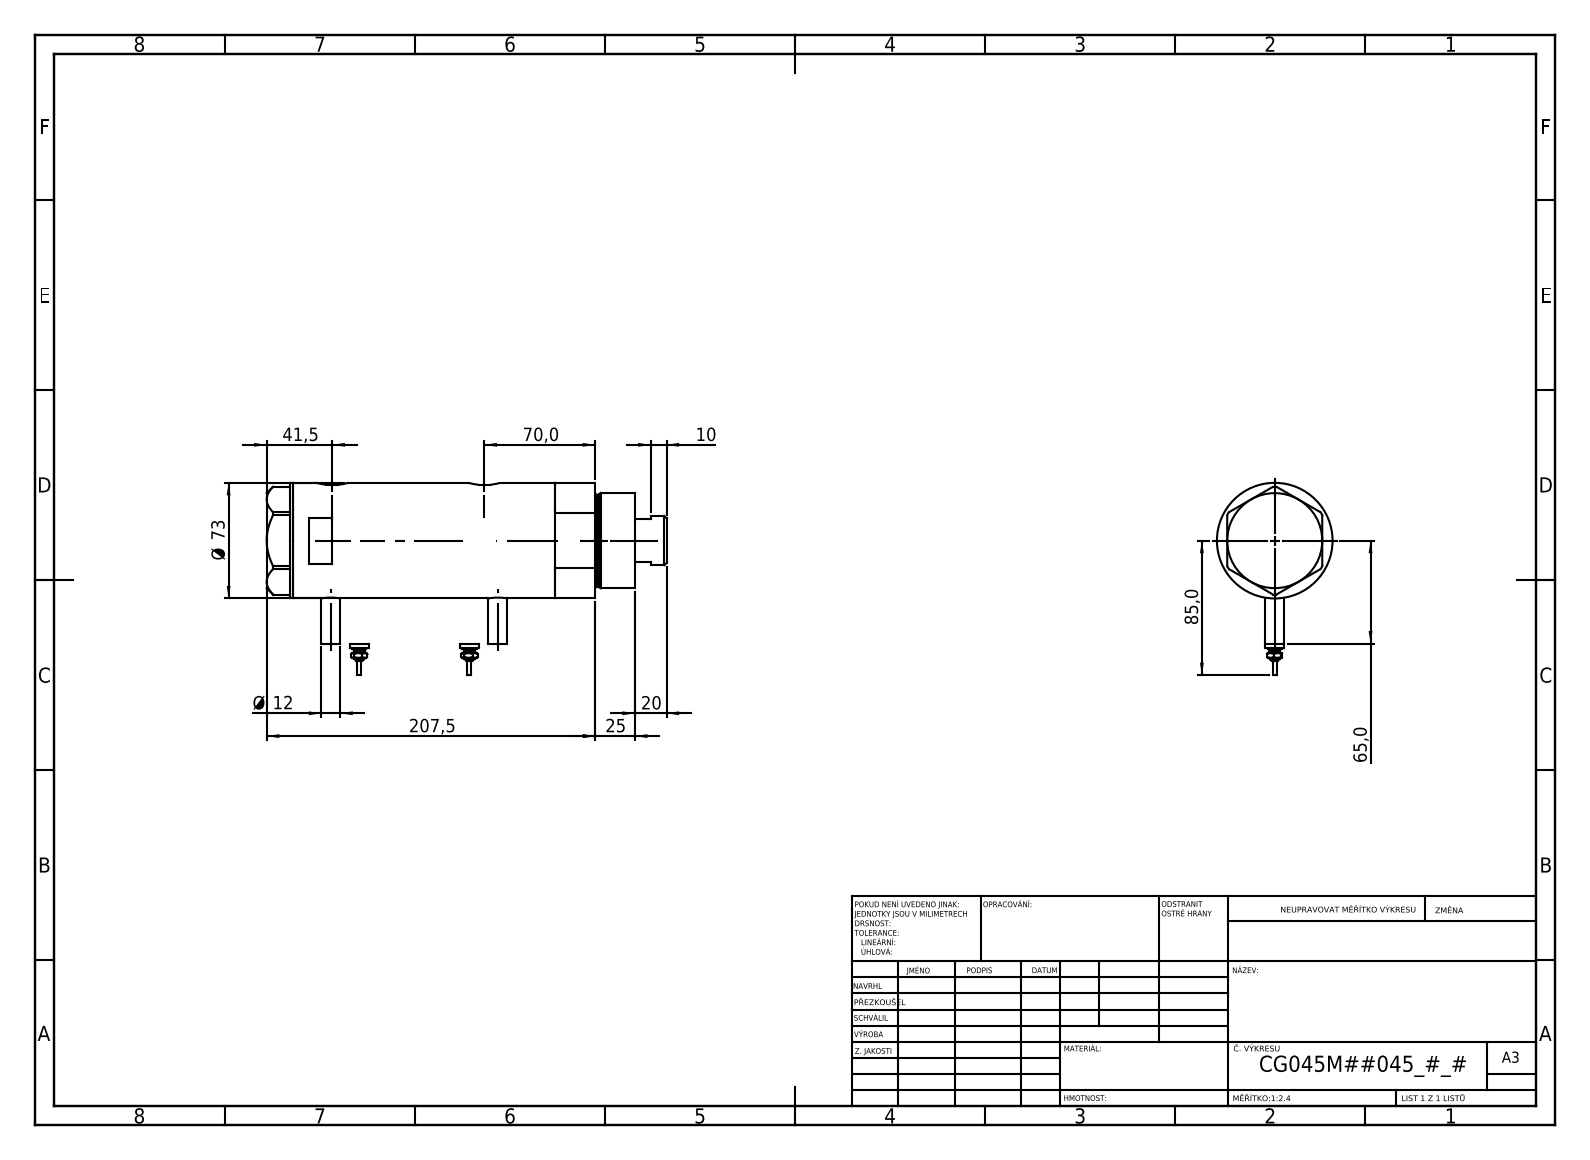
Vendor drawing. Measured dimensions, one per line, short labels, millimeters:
name: Switch; V270CG_VC; V270CG_BACK; V270CG_MIDDLE (+1 more)
written by: SolidWorks 2019 (CONFIG_CONTROL_DESIGN)
unit: mm
bodies: 6 solids, 212 faces (77 planar, 71 cylindrical, 64 other)
size: 252.5 × 121.5 × 73
volume: 896 090 mm³; area: 151 933 mm²
holes: 2× ⌀12.5, 2× ⌀13.16, 1× ⌀10.5, 1× ⌀32, 1× ⌀33.5, 1× ⌀45, 1× ⌀48, 1× ⌀64
bosses: 4× ⌀12, 2× ⌀9, 2× ⌀7, 2× ⌀4.5, 2× ⌀2.5, 1× ⌀73, 1× ⌀60, 1× ⌀58
rounds: 2× R10
face distances: 95, 121, 26, 16.5, 42.5, 137.5, 2, 216, 232.5, 190
hole spacings: 1, 8.5, 96, 97, 104.5, 105.5
